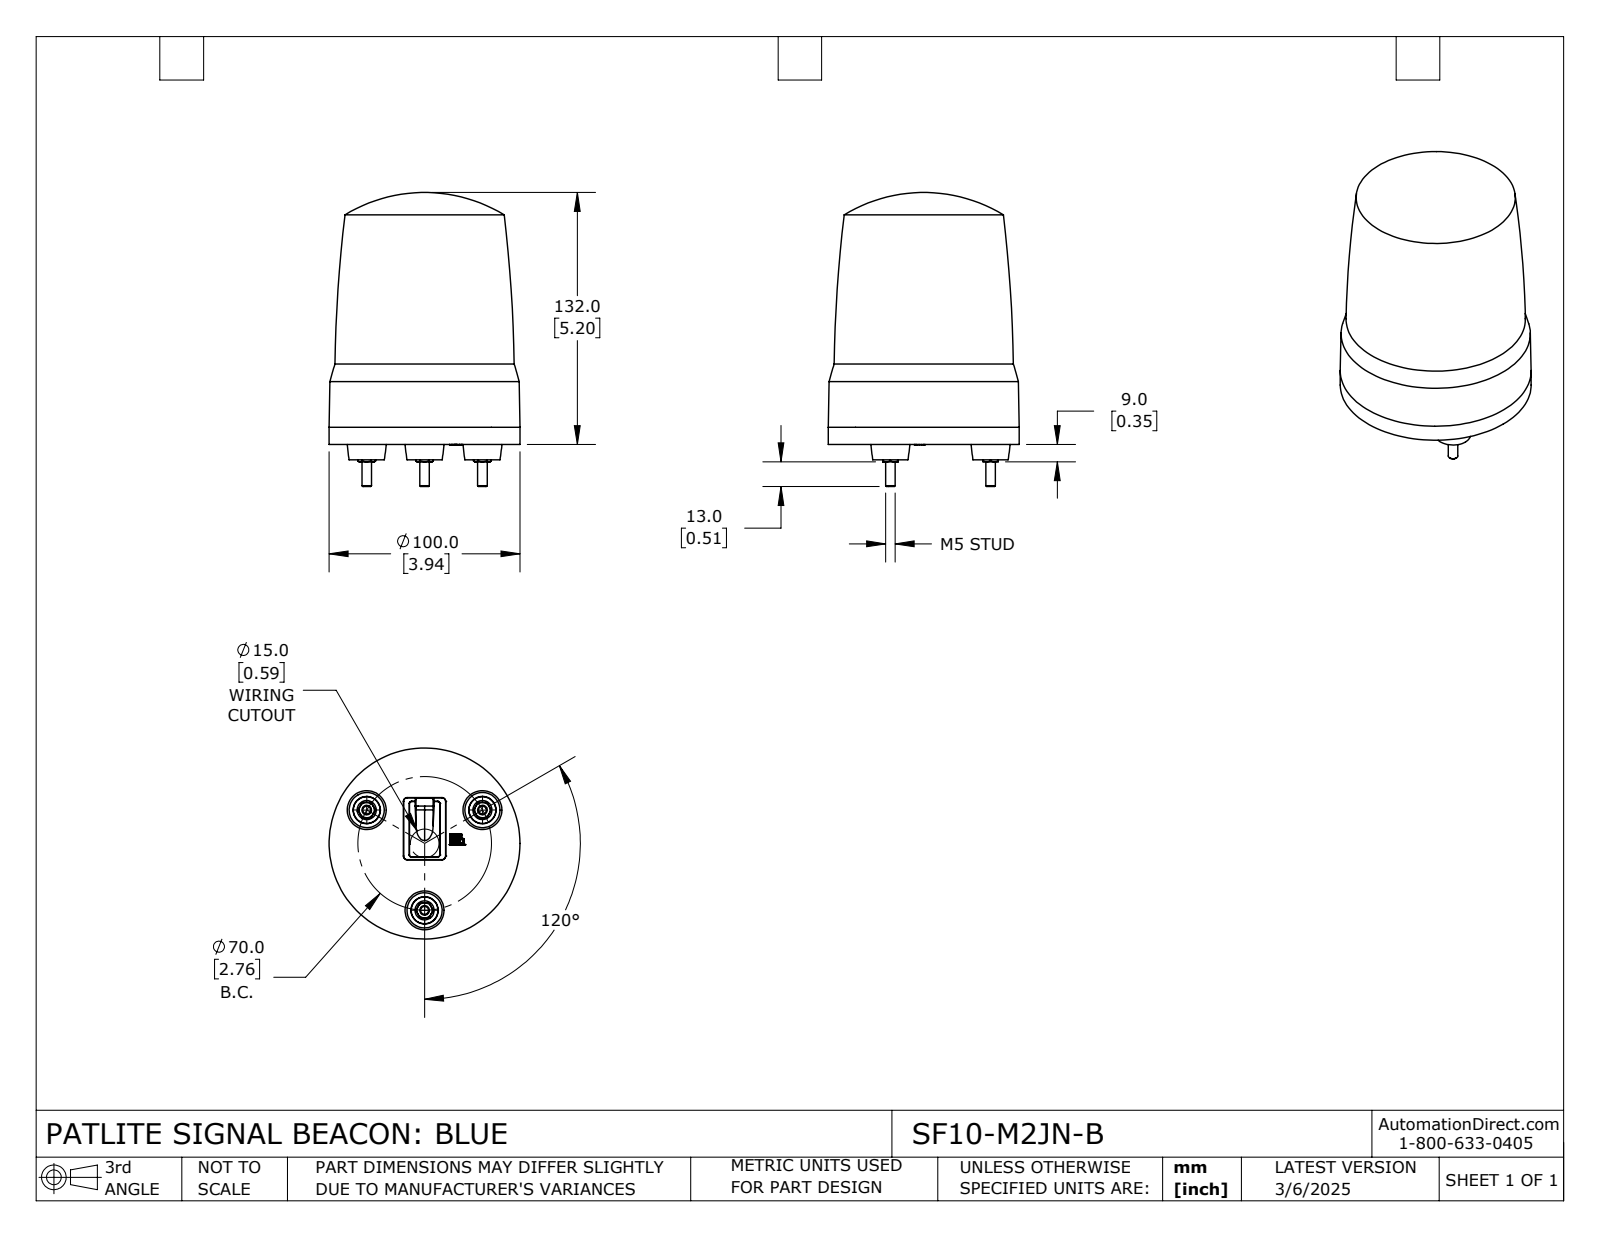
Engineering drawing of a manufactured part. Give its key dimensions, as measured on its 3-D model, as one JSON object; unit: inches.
{"part_name": "SF10-M2JN-B", "step_written_by": "SolidWorks 2024 (CONFIG_CONTROL_DESIGN)", "units": "inches", "bodies": {"solids": 1, "faces": 327, "planar": 159, "cylindrical": 14, "other": 154}, "overall_size": [6.063, 3.937, 3.937], "volume_in3": 52.48, "surface_area_in2": 81.51, "round_bosses_or_shafts": [[0.394, 3], [0.197, 3], [3.937, 1]], "face_to_face_distances": [0.315, 0.033, 0.348, 0.063, 0.411, 0.096, 0.15, 0.165, 0.199, 0.262]}
